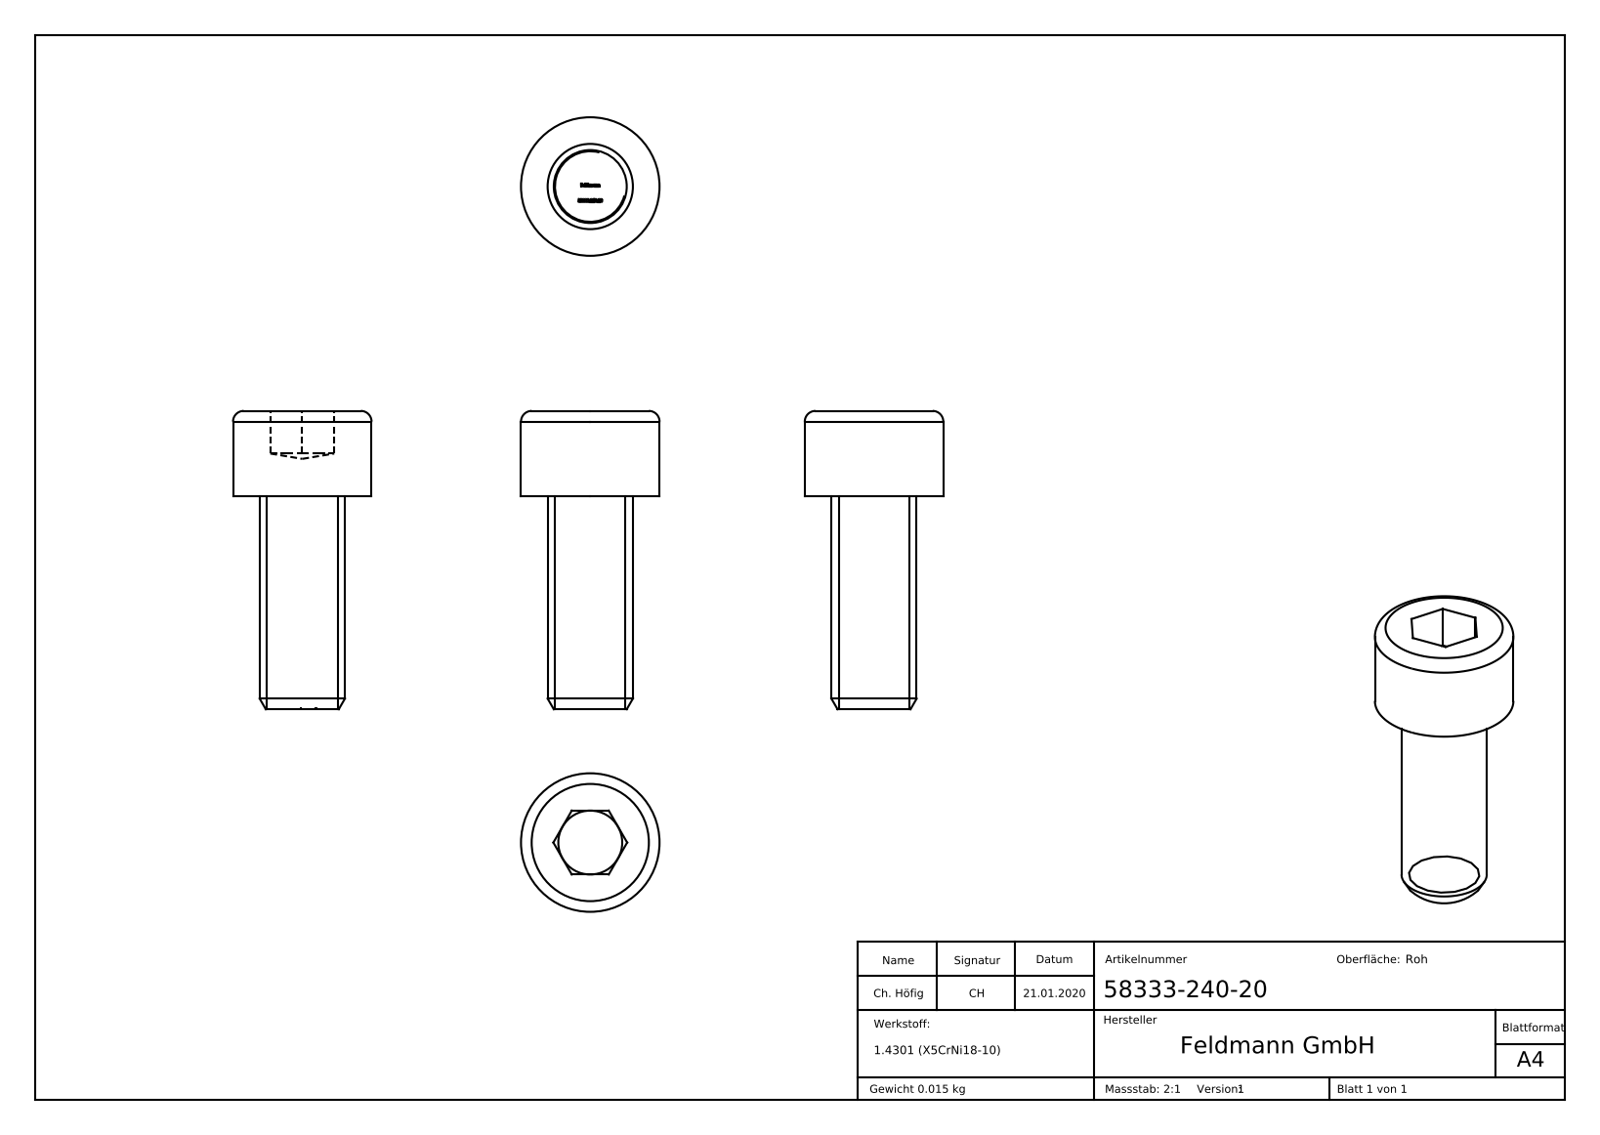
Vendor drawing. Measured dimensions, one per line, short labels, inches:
name: 58333-240-20
written by: SolidWorks 2015 (CONFIG_CONTROL_DESIGN)
unit: in
bodies: 1 solid, 295 faces (145 planar, 2 cylindrical, 148 other)
size: 1.142 × 0.512 × 0.512
volume: 0.117 in³; area: 1.784 in²
bosses: 1× ⌀0.512, 1× ⌀0.315
face distances: 0.315, 0.236, 0.787, 1.102, 0.157, 0.945, 0.783, 0.941, 1.098, 0.021
